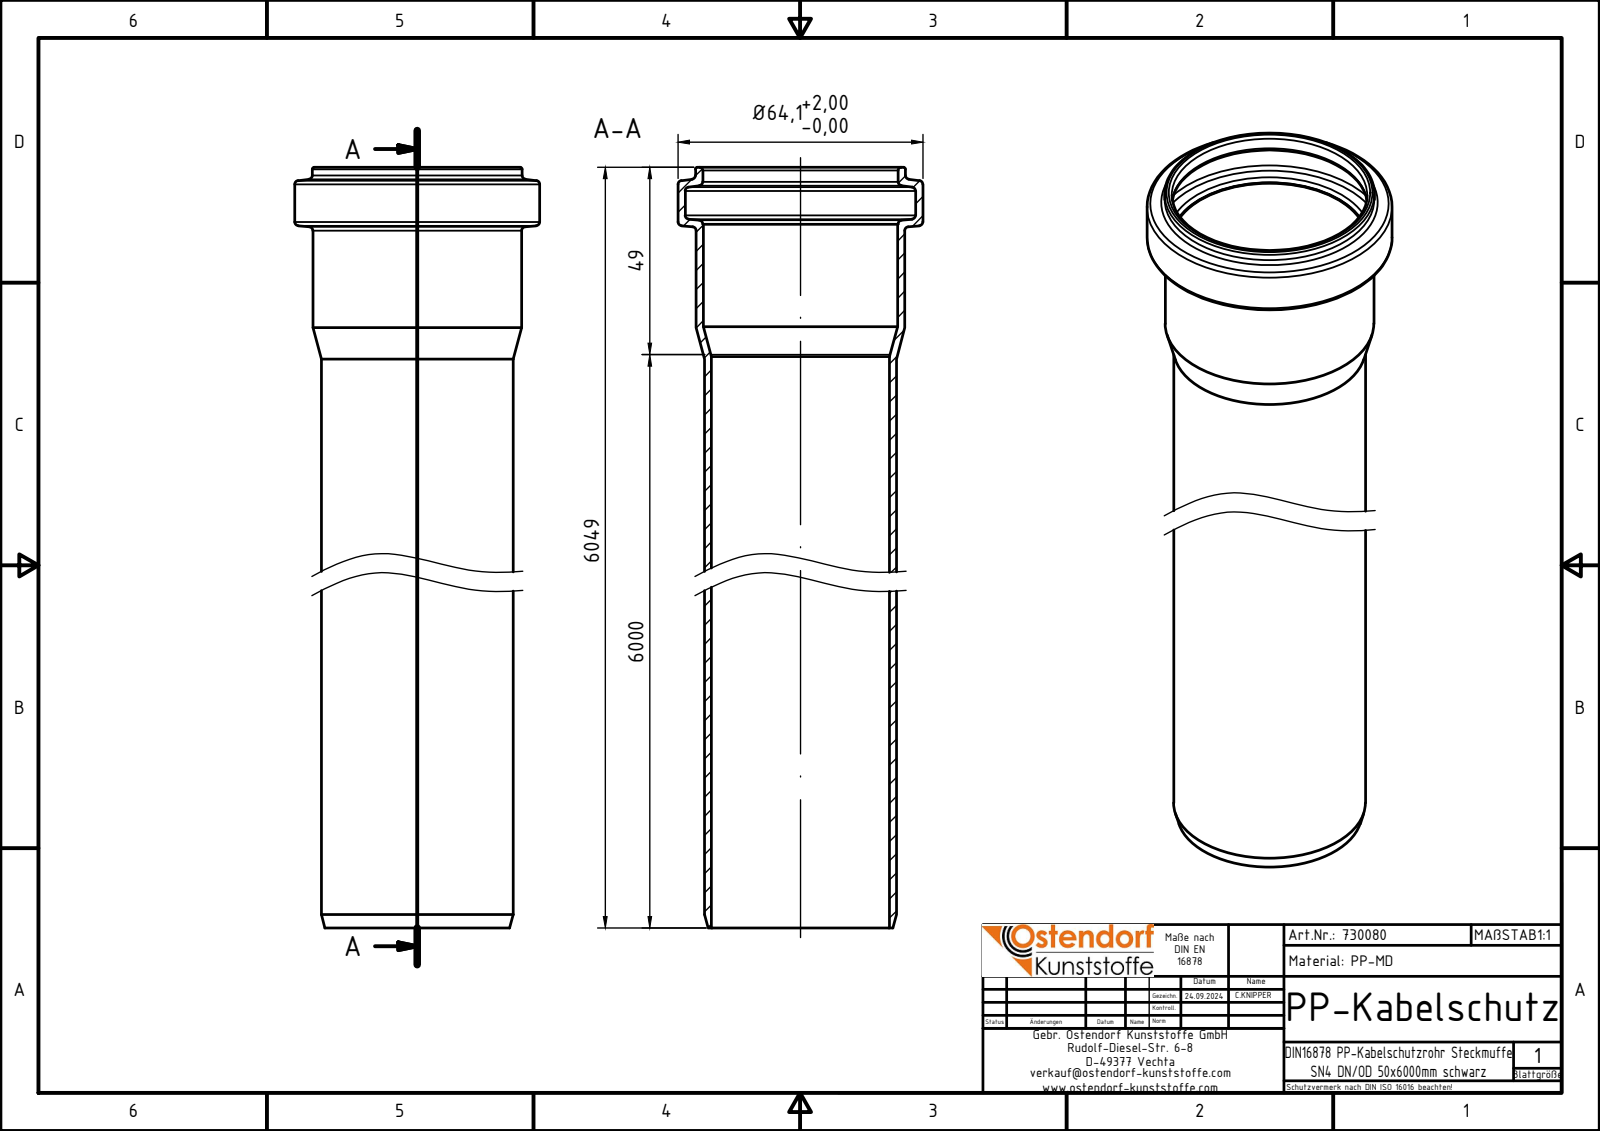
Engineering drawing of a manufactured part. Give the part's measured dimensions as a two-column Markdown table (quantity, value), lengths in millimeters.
| quantity | value |
| --- | --- |
| part name | 730080z |
| STEP written by | Autodesk Inventor 2024 (AUTOMOTIVE_DESIGN) |
| units | millimeters |
| bodies | 1 solid, 29 faces (3 planar, 9 cylindrical, 17 other) |
| overall size | 6049 × 64.1 × 64.1 |
| volume | 1 661 000 mm³ |
| surface area | 1 844 000 mm² |
| round holes (diameter × count) | 46.6 × 1, 50.8 × 1, 51.1 × 1, 60.3 × 1 |
| round bosses / shafts (diameter × count) | 64.1 × 1, 54.9 × 1, 54.6 × 1, 50.2 × 1 |
| main face-to-face distances | 6049, 6034.1, 14.9 |
